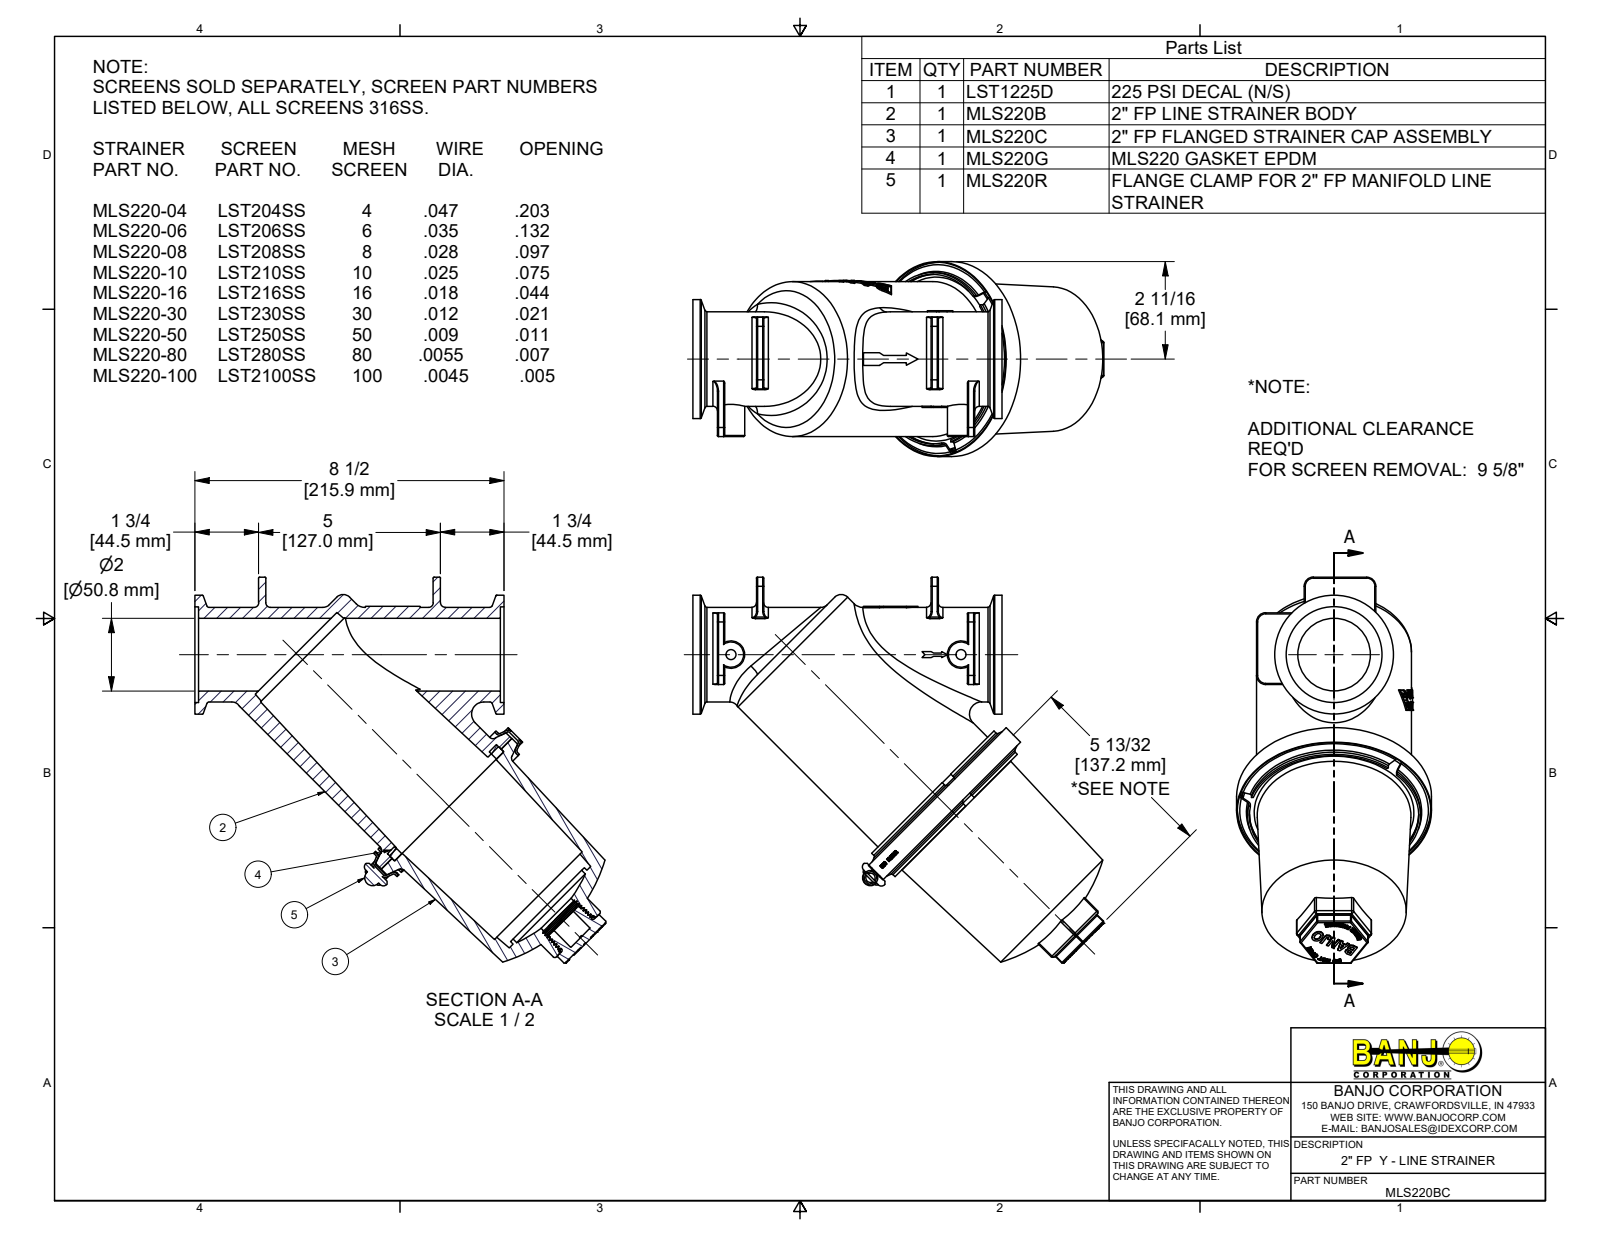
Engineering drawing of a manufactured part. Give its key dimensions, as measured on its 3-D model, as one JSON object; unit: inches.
{"part_name": "MLS220BC; MLS220B; LST100-D 150; MLS220R (+5 more)", "step_written_by": "Autodesk Inventor 2019 (AUTOMOTIVE_DESIGN)", "units": "inches", "bodies": {"solids": 7, "faces": 3002, "planar": 1450, "cylindrical": 427, "other": 1125}, "overall_size": [11.299, 10.609, 5.359], "volume_in3": 70.07, "surface_area_in2": 498.8, "round_holes": [[0.275, 2], [4.658, 2], [0.25, 1], [0.327, 1], [0.454, 1], [0.462, 1], [0.641, 1], [0.75, 1], [1.165, 1], [2, 1], [2.63, 1], [2.67, 1]], "round_bosses_or_shafts": [[4.758, 2], [5.359, 1], [5.08, 1], [5.07, 1], [4.26, 1], [4.24, 1], [3.27, 1], [2.87, 1]], "partial_cylinders_radius": [[0.03, 50], [0.06, 22], [0.125, 4], [0.25, 4], [0.028, 2], [0.039, 2], [0.041, 2], [0.056, 2]], "face_to_face_distances": [0.1, 0.2, 8.4, 0.281, 0.181, 5.949, 5.849, 5.668, 1.95, 6.55], "hole_center_spacings": [1.281, 2.522, 3.661, 3.891, 4.281, 4.32, 5.153, 6.325]}
